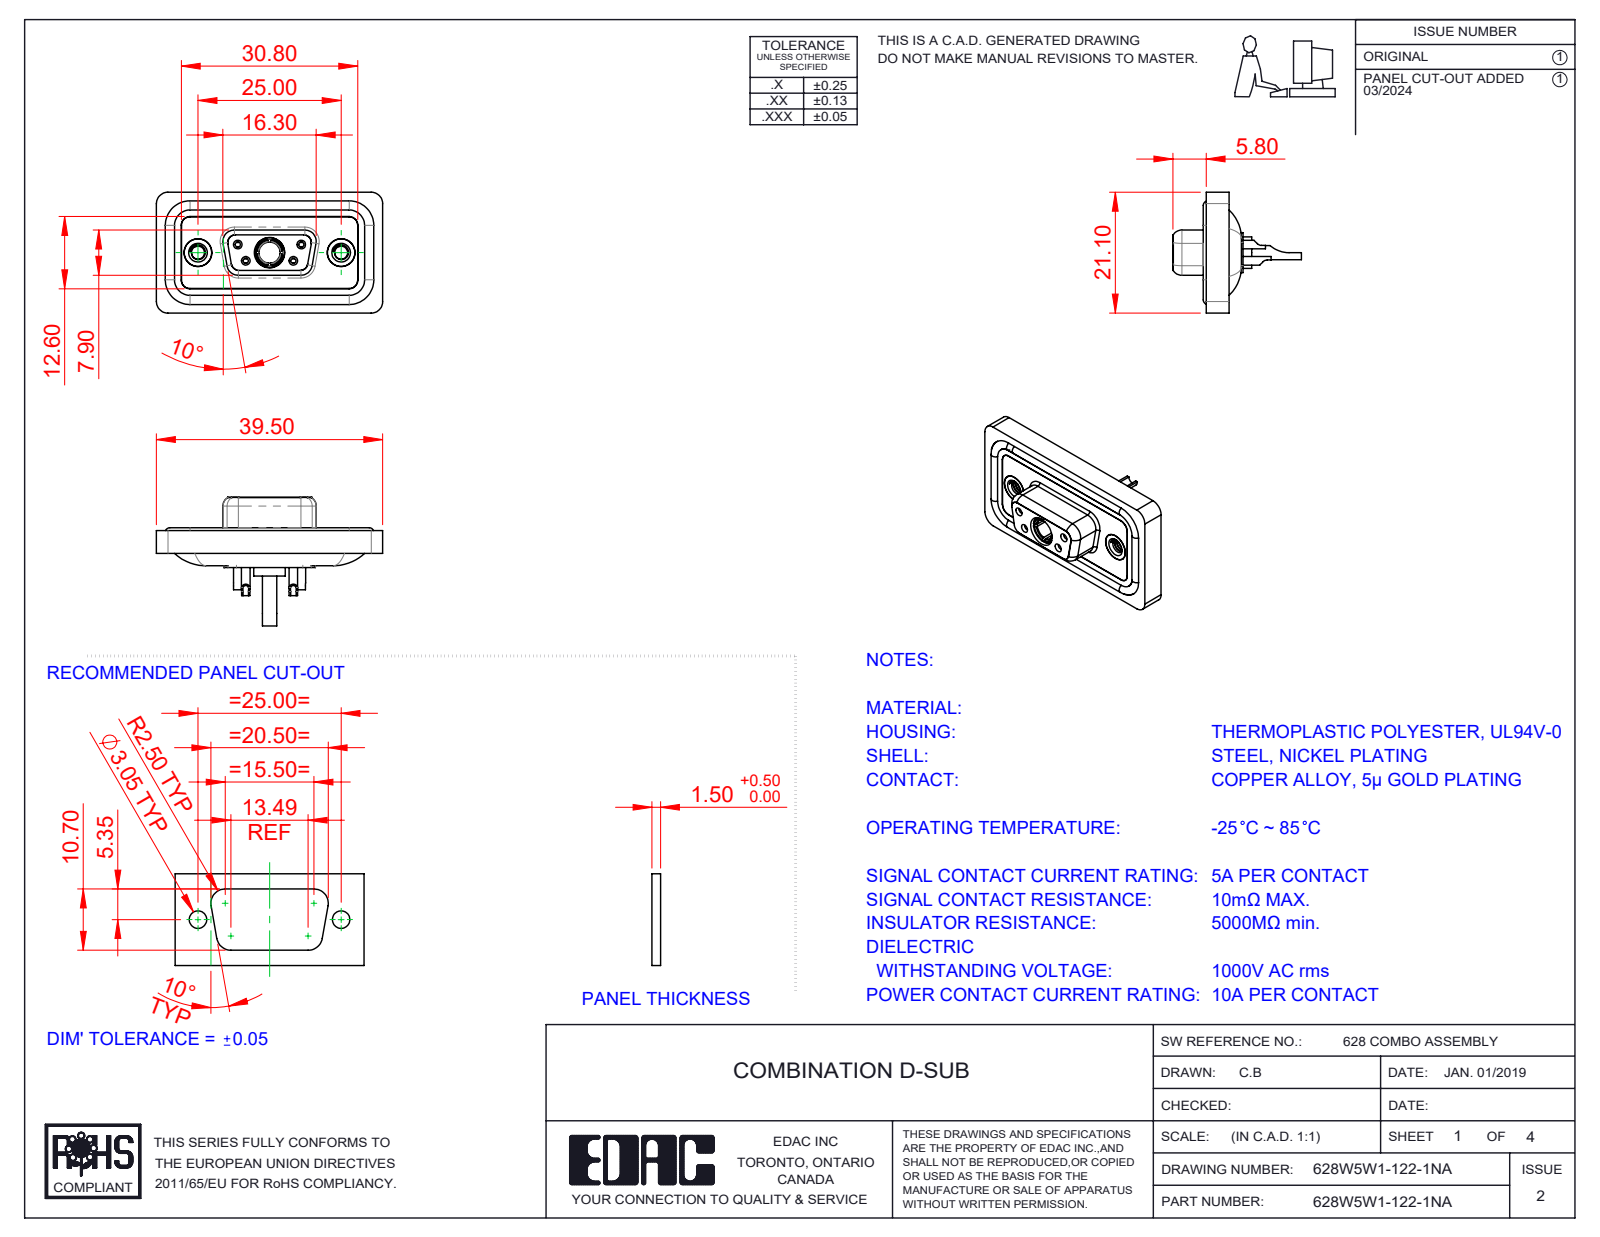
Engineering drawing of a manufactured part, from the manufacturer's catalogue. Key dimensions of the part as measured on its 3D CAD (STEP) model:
Part name (STEP PRODUCT): Power Socket_10A SC; 628Combo Contact Row 1_22; 628Combo Housing_5W1; 628Combo Contact Row 2_22 (+5 more)
STEP written by: SolidWorks 2023 (CONFIG_CONTROL_DESIGN)
Units: millimetres
Bodies: 13 solids, 683 faces (204 planar, 300 cylindrical, 179 other)
Overall size (bounding box): 39.5 × 22.45 × 21.1
Volume: 4 774 mm³ · Surface area: 7 723 mm²
Round holes (diameter × count): ⌀0.9 ×4, ⌀1 ×4, ⌀1.1 ×4, ⌀1.5 ×4, ⌀2 ×4, ⌀4.85 ×3, ⌀1.6 ×2, ⌀1.7 ×2, ⌀2.26 ×2, ⌀4 ×2, ⌀4.05 ×2, ⌀5 ×2
Round bosses / shafts (diameter × count): ⌀1.6 ×6, ⌀2.2 ×4, ⌀4.95 ×2, ⌀4.8 ×2, ⌀5.5 ×1, ⌀5.2 ×1, ⌀4.96 ×1, ⌀4.75 ×1
Partial cylindrical surfaces — rounded edges, fillets, slot ends (radius × count): R1.5 ×22, R2 ×18, R1.35 ×8, R1.6 ×8, R1 ×6, R0.25 ×4, R0.5 ×4, R0.6 ×4
Main face-to-face distances: 0.4, 2.9, 1.8, 1.1, 1.6, 0.5, 5.65, 7.45, 5.35, 3.6
Hole centre spacings: 3.16, 5.72, 7.1, 12.5, 18.1, 4.39, 4.4, 8.31
